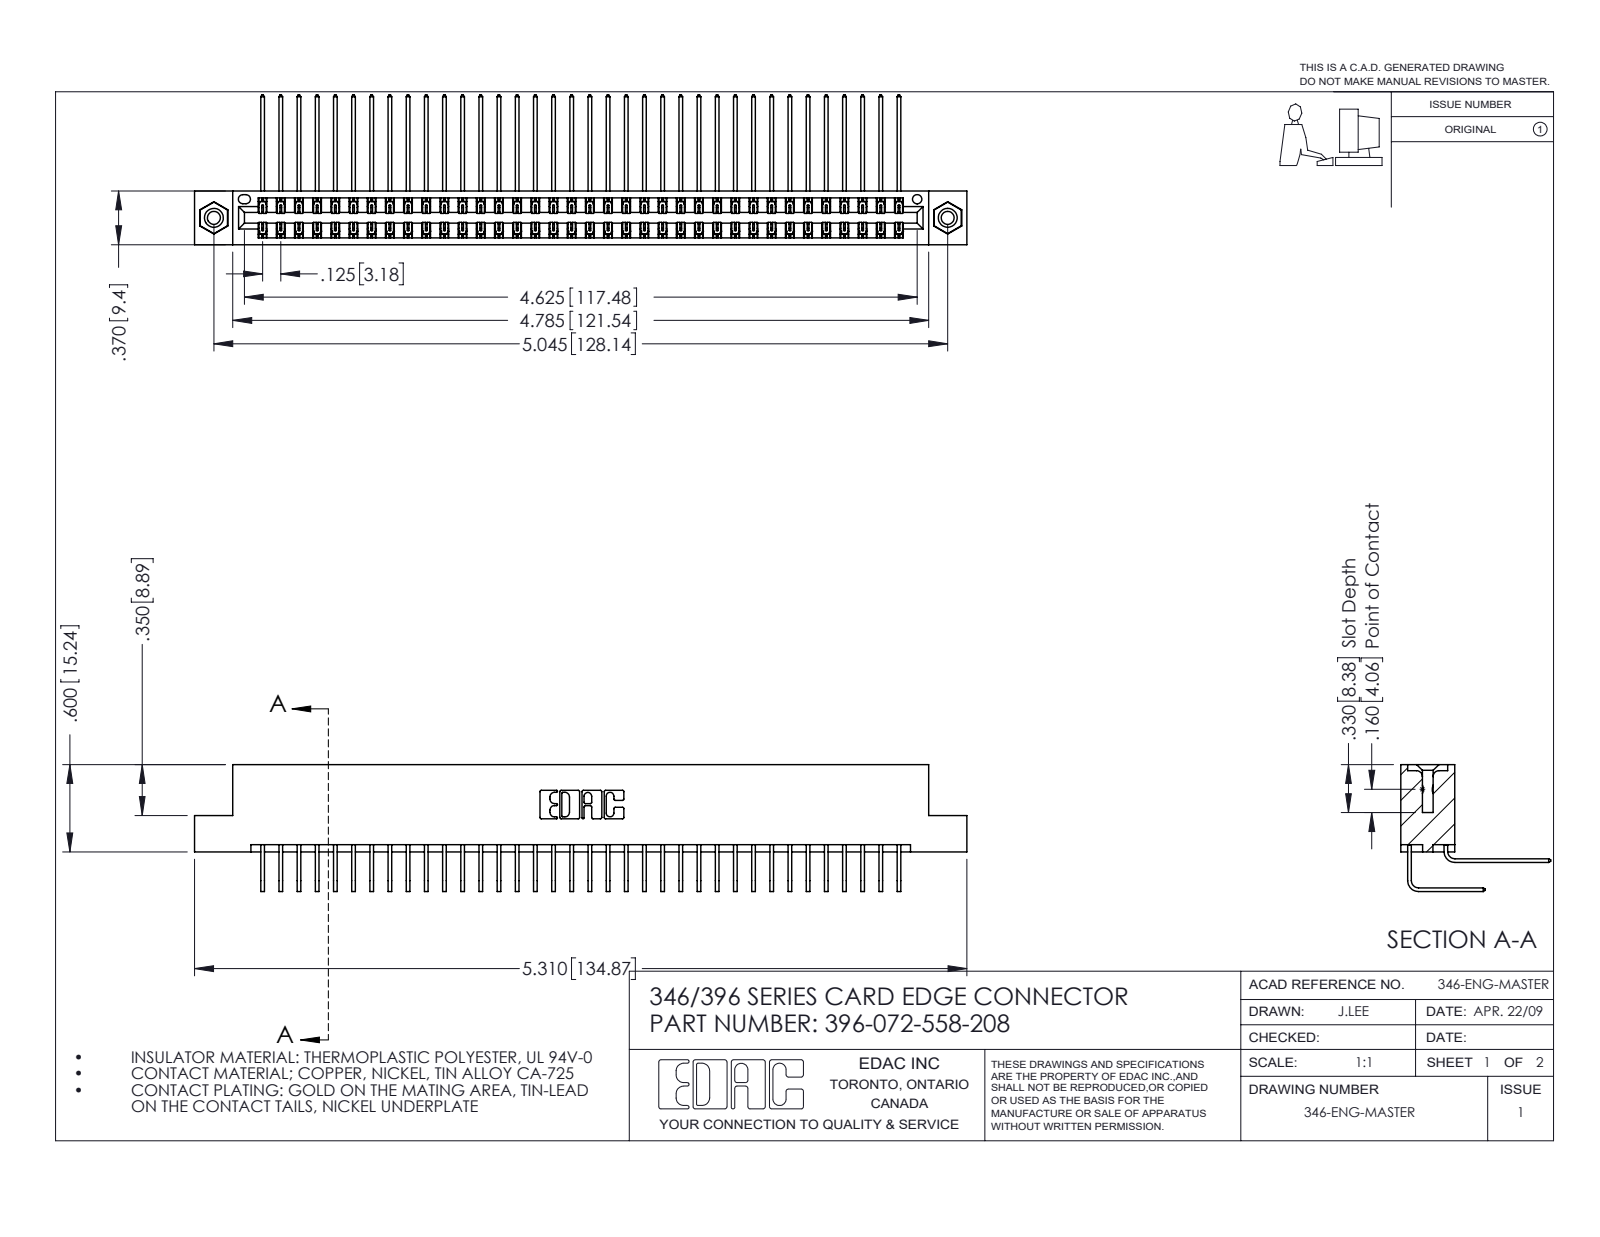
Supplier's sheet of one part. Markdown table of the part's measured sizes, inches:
| quantity | value |
| --- | --- |
| part name | 346 Part_Flush Mounting Lugs - 0.156 Dia-TI; 345-292-001_558 559 Tail - 1; 396-072-558-208; 345-250-001_345-250-003-102 (+1 more) |
| STEP written by | SolidWorks 2016 (CONFIG_CONTROL_DESIGN) |
| units | inches |
| bodies | 75 solids, 4070 faces (2772 planar, 1282 cylindrical, 16 other) |
| overall size | 5.31 × 1.03 × 0.873 |
| volume | 0.825 in³ |
| surface area | 31.77 in² |
| round holes (diameter × count) | 0.089 × 2, 0.125 × 2, 0.156 × 2, 0.064 × 1 |
| round bosses / shafts (diameter × count) | 0.155 × 2 |
| partial cylindrical surfaces (radius × count) | 0.006 × 108, 0.01 × 22, 0.007 × 6, 0.031 × 6, 0.026 × 3, 0.014 × 2, 0.022 × 2, 0.024 × 2 |
| main face-to-face distances | 0.048, 0.322, 0.025, 0.37, 0.25, 0.072, 0.298, 0.275, 0.148, 0.222 |
| hole center spacings | 0.246, 4.836, 5.045 |
